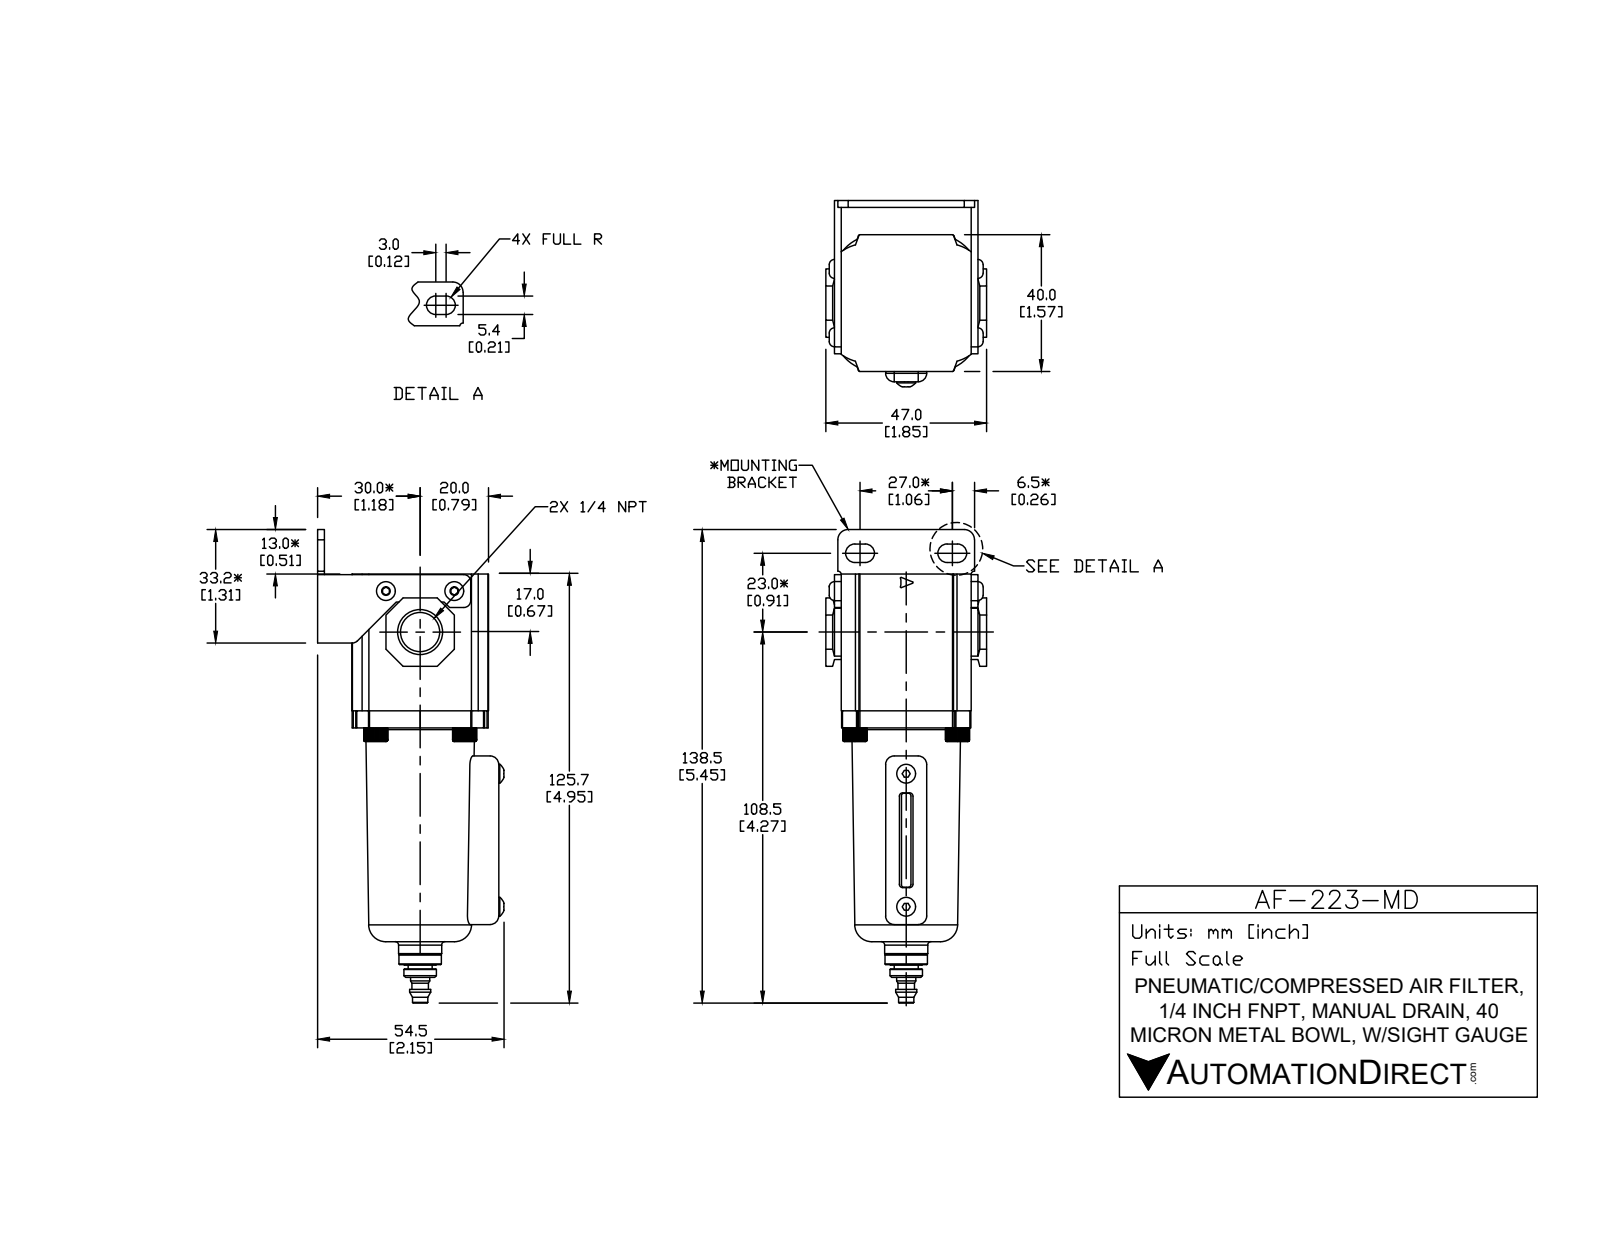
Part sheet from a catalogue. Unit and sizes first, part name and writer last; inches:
Units: inches
Overall size (bounding box): 5.451 × 2.165 × 1.85
Round holes (diameter × count): ⌀0.134 ×2, ⌀0.118 ×1, ⌀0.438 ×1
Round bosses / shafts (diameter × count): ⌀0.276 ×5, ⌀0.217 ×2, ⌀0.496 ×1, ⌀0.472 ×1, ⌀0.375 ×1, ⌀0.374 ×1, ⌀0.244 ×1, ⌀0.22 ×1
Partial cylindrical surfaces — rounded edges, fillets, slot ends (radius × count): R0.012 ×12, R0.051 ×8, R0.098 ×8, R0.079 ×5, R0.02 ×4, R0.039 ×4, R0.106 ×4, R0.469 ×4
Main face-to-face distances: 1.575, 0.079, 1.496, 0.315, 0.394, 1.969, 1.89, 0.512, 0.591, 1.654
Hole centre spacings: 0.615, 0.787
Volume: 7.253 in³ · Surface area: 48.26 in²
Bodies: 9 solids, 390 faces (217 planar, 109 cylindrical, 64 other)
Part name (STEP PRODUCT): AF-223-MD
STEP written by: SolidWorks 2015 (CONFIG_CONTROL_DESIGN)
